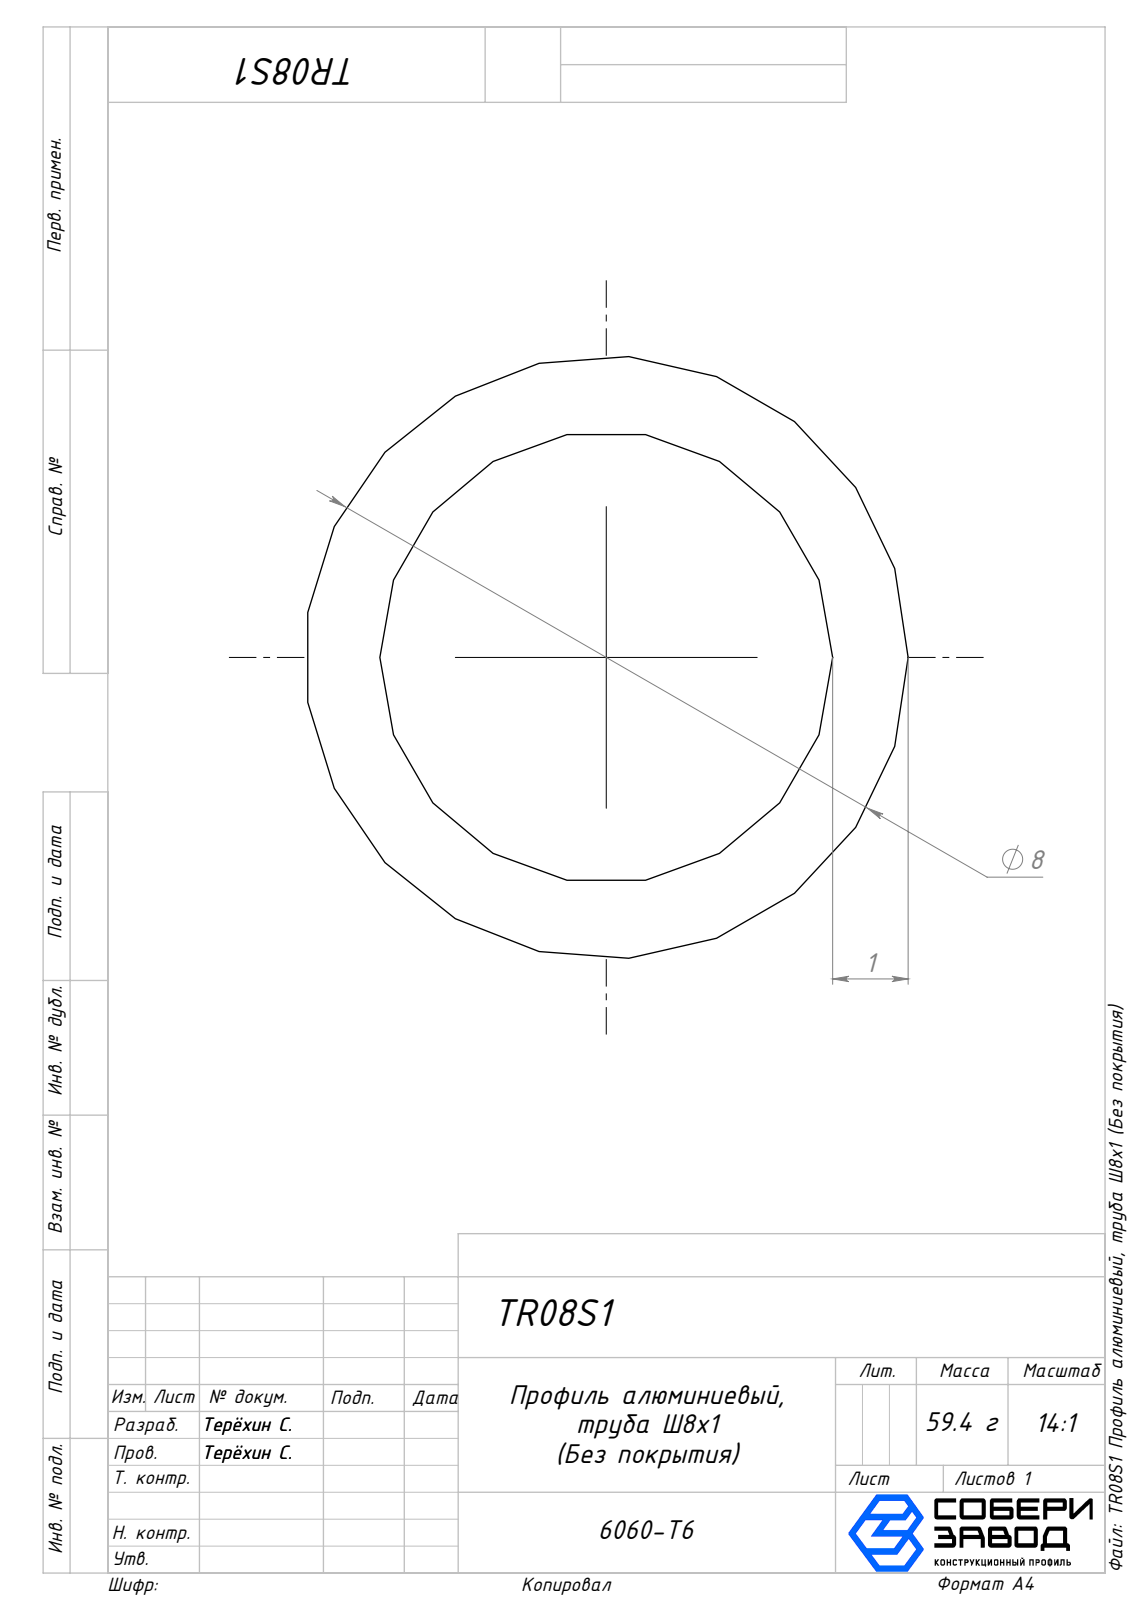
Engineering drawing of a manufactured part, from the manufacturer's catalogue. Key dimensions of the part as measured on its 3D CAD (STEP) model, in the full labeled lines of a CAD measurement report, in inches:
Part name (STEP PRODUCT): Сборка8; TR08S1 Профиль алюминиевый, труба Ø8х1 (Без покрытия)_00
STEP written by: SolidWorks 2025 (AUTOMOTIVE_DESIGN)
Units: inches
Bodies: 1 solid, 6 faces (2 planar, 4 cylindrical, 0 other)
Overall size (bounding box): 39.37 × 0.315 × 0.315
Volume: 1.342 in³ · Surface area: 68.24 in²
Round holes (diameter × count): ⌀0.236 ×1
Round bosses / shafts (diameter × count): ⌀0.315 ×1
Main face-to-face distances: 39.37
